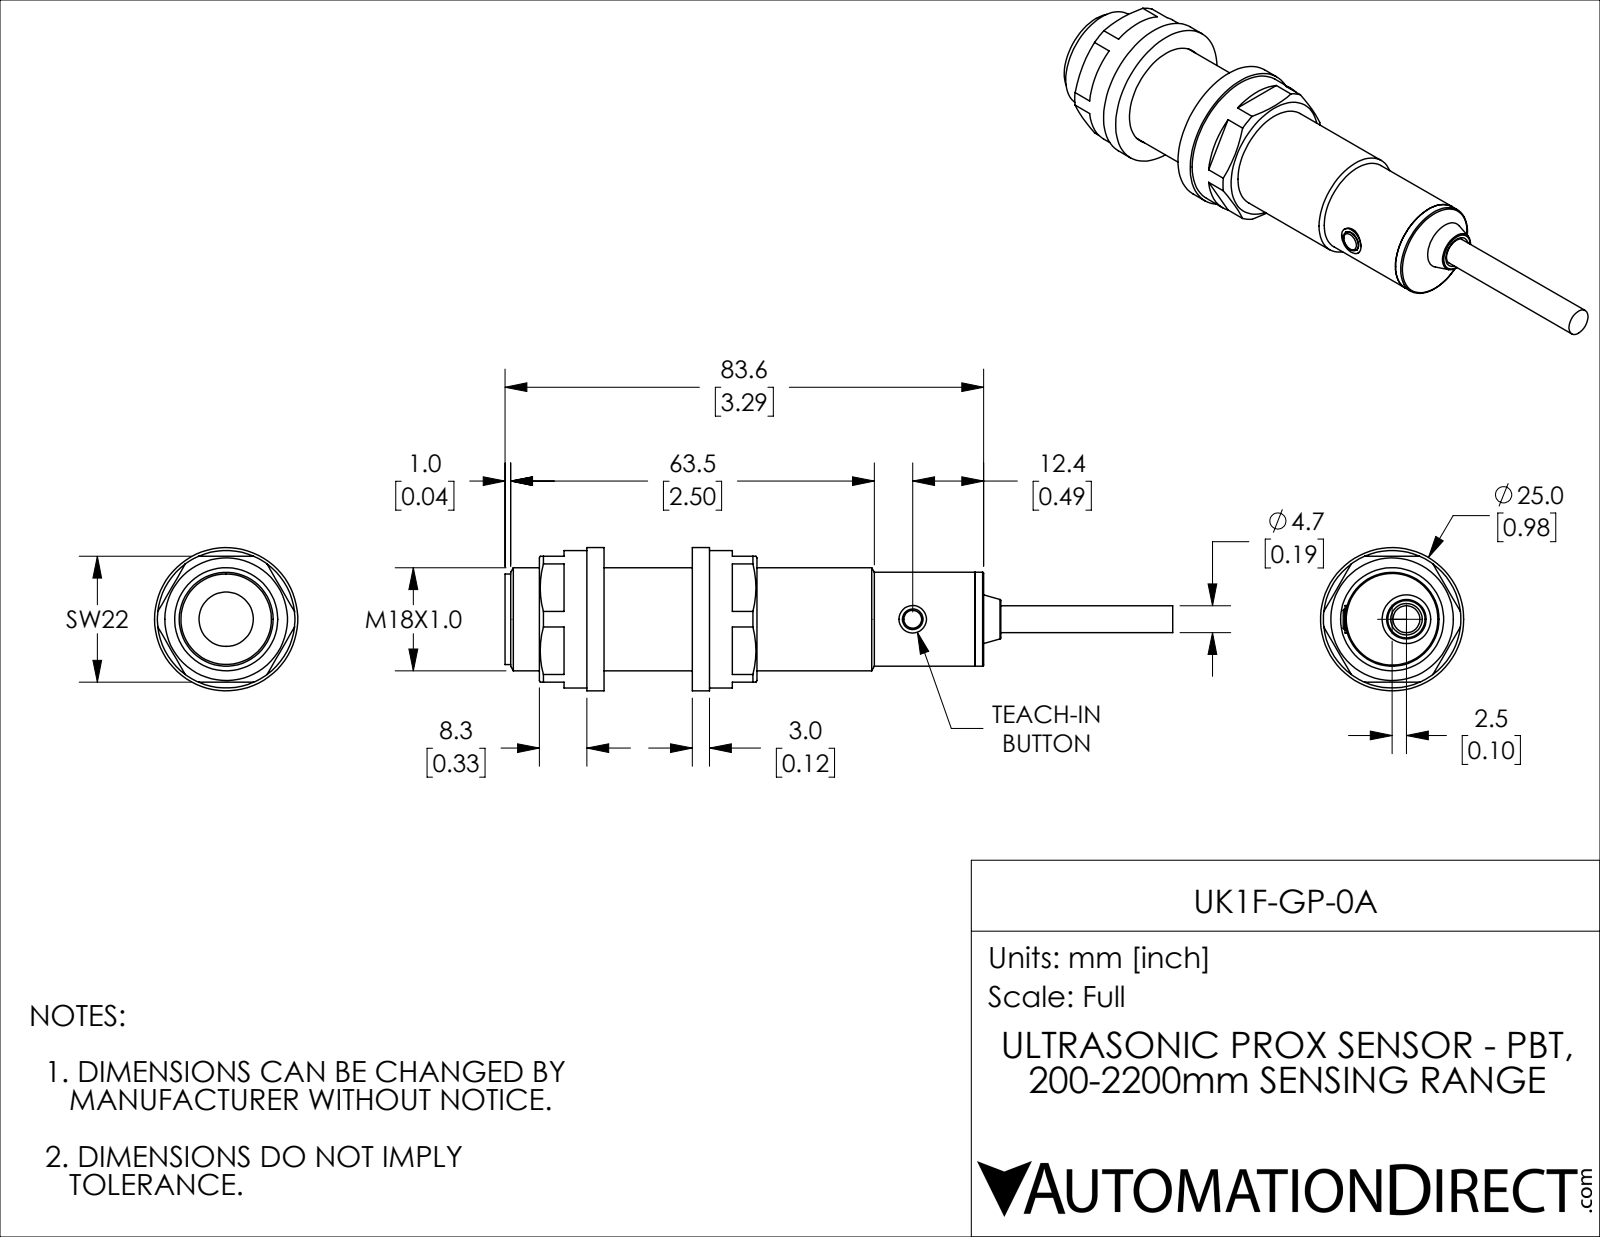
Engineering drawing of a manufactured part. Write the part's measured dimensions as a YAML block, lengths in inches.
part_name: "UK1F-GP-0A"
step_written_by: "SolidWorks 2018 (AUTOMOTIVE_DESIGN)"
units: inches
bodies: {solids: 10, faces: 107, planar: 49, cylindrical: 40, other: 18}
overall_size: [4.591, 0.984, 0.984]
volume: 1.539
surface_area: 17.7
round_holes:
  - {diameter: 0.185, count: 2}
  - {diameter: 0.142, count: 1}
  - {diameter: 0.374, count: 1}
  - {diameter: 0.709, count: 1}
  - {diameter: 0.717, count: 1}
round_bosses_or_shafts:
  - {diameter: 0.984, count: 1}
  - {diameter: 0.945, count: 1}
  - {diameter: 0.646, count: 1}
  - {diameter: 0.622, count: 1}
  - {diameter: 0.213, count: 1}
  - {diameter: 0.189, count: 1}
face_to_face_distances: [0.118, 0.724, 0.843, 2.669, 1.827, 0.524, 1.366, 3.193, 0.642, 2.551]
hole_center_spacings: [0.098]
